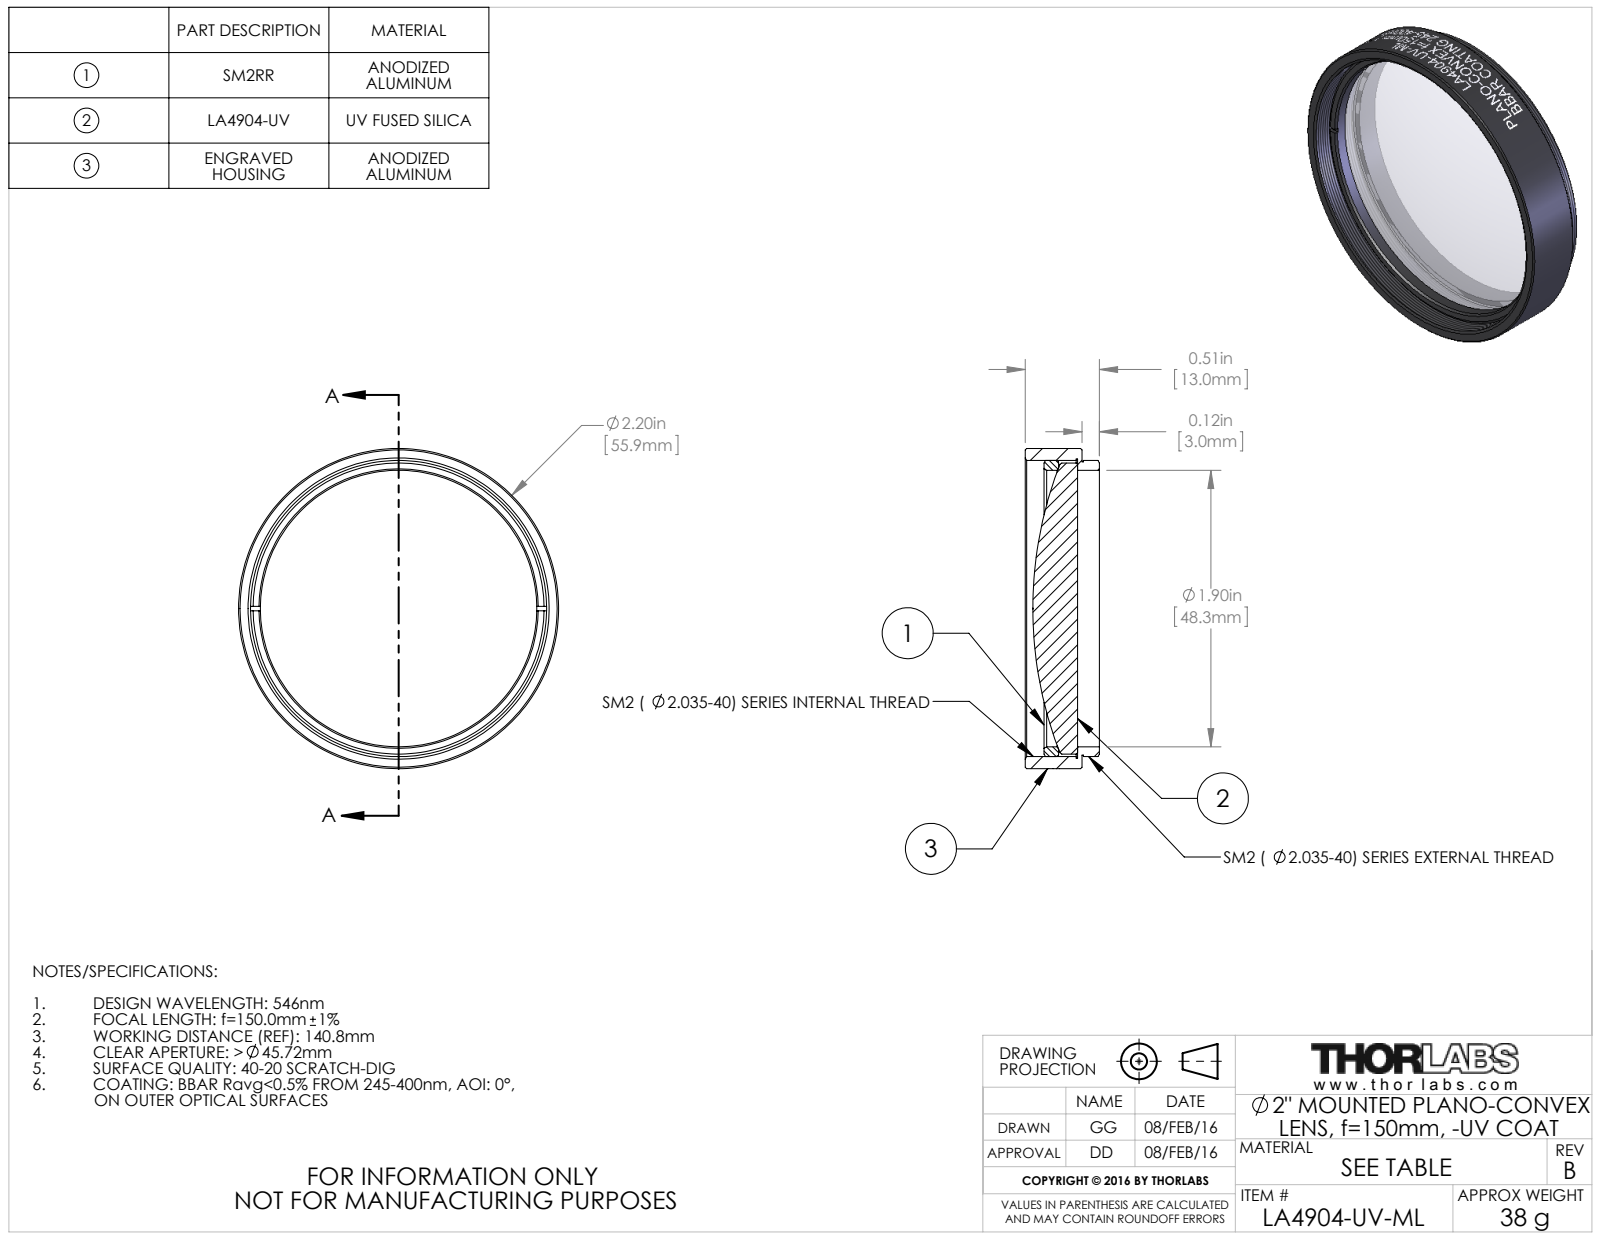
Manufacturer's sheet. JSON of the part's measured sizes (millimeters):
{"part_name": "TTN039434-E0W", "step_written_by": "SolidWorks 2014 (CONFIG_CONTROL_DESIGN)", "units": "millimeters", "bodies": {"solids": 3, "faces": 149, "planar": 16, "cylindrical": 109, "other": 24}, "overall_size": [55.88, 55.88, 12.95], "volume_mm3": 16138, "surface_area_mm2": 11385, "round_holes": [[48.26, 1], [52.2, 1]], "round_bosses_or_shafts": [[55.88, 1], [51.69, 1], [51.18, 1], [50.8, 1]], "face_to_face_distances": [0.76, 9.91, 9.15, 3.05, 3.81, 12.96, 7.13, 4.08, 3.32, 5.83]}
